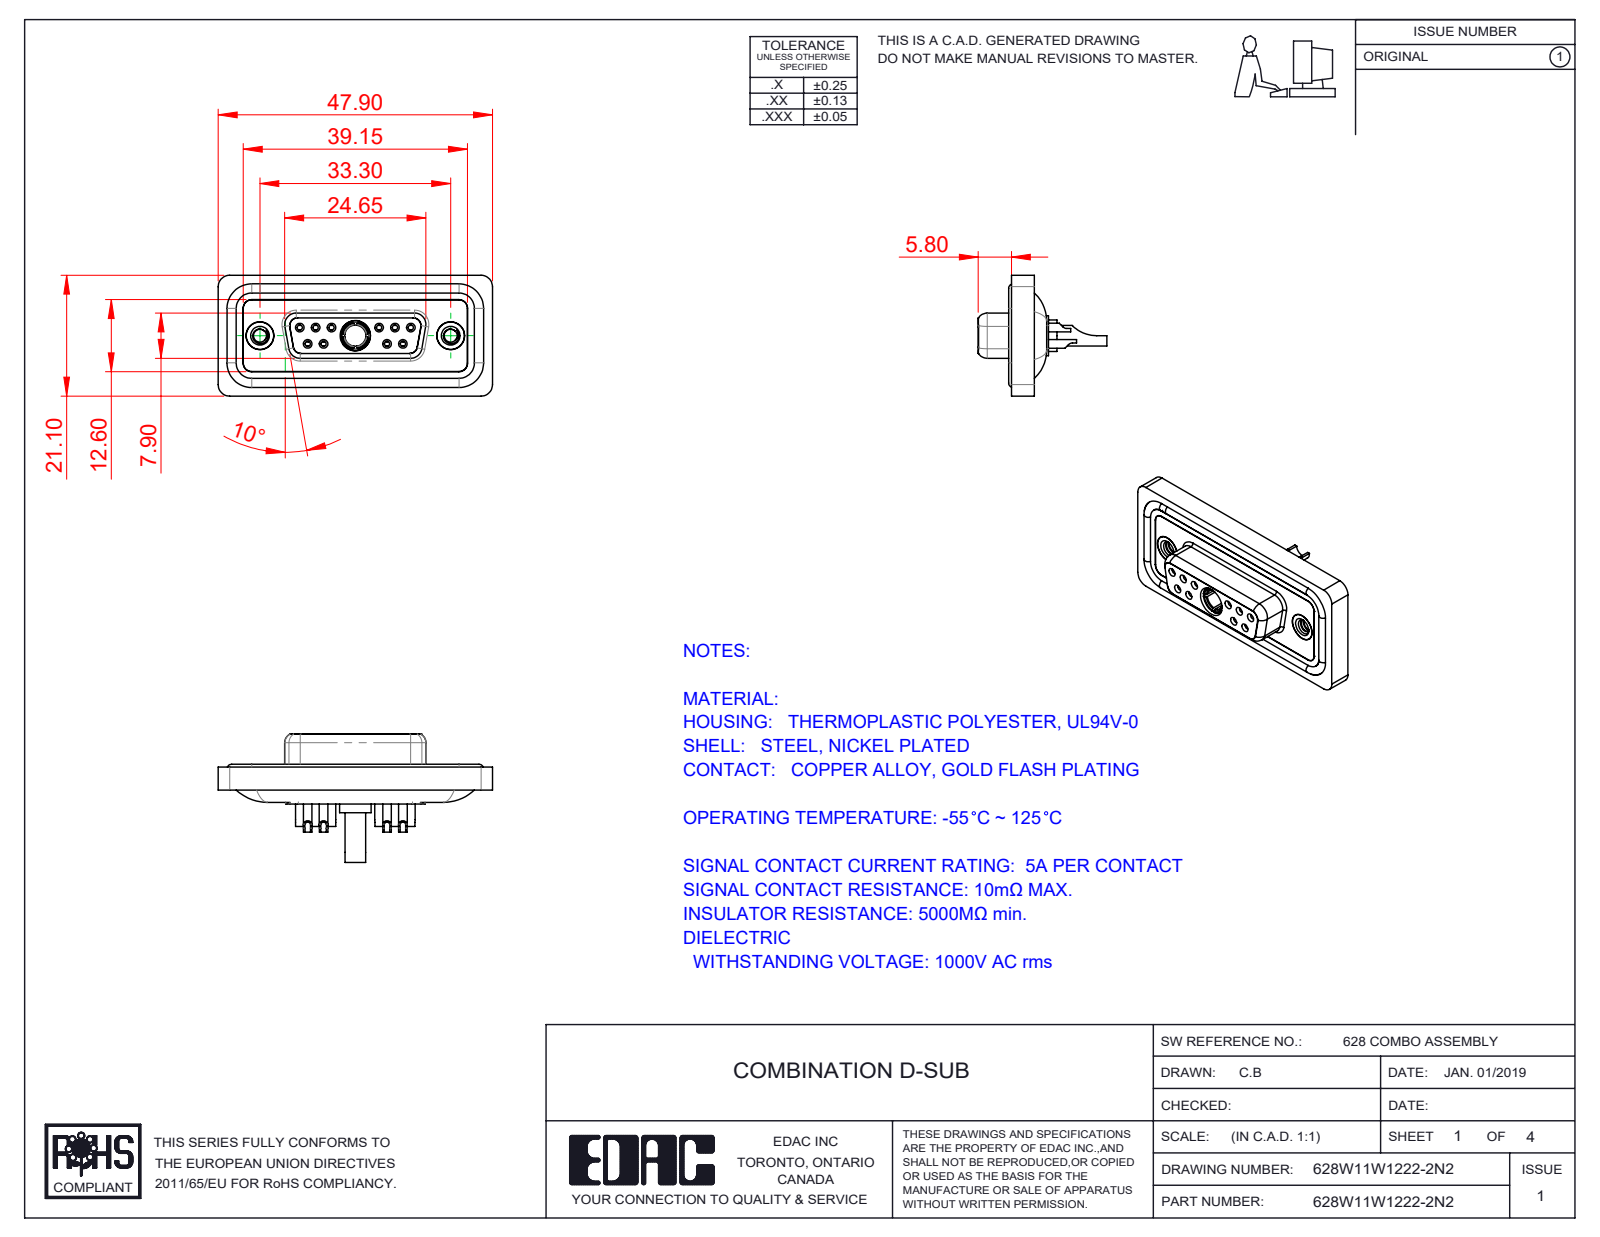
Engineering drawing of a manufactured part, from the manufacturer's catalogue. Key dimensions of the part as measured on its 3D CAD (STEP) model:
Part name (STEP PRODUCT): 628Combo Shell Rear_15 Contacts; Power Socket_20A SC; 628Combo Shell Front_15 Contacts; 628W11W1222-2N2 (+5 more)
STEP written by: SolidWorks 2020 (CONFIG_CONTROL_DESIGN)
Units: millimetres
Bodies: 19 solids, 1017 faces (307 planar, 424 cylindrical, 286 other)
Overall size (bounding box): 47.9 × 22.45 × 21.1
Volume: 6 158 mm³ · Surface area: 10 215 mm²
Round holes (diameter × count): ⌀0.9 ×10, ⌀1 ×10, ⌀1.1 ×10, ⌀1.5 ×10, ⌀2 ×10, ⌀1.7 ×6, ⌀1.6 ×4, ⌀4.85 ×3, ⌀2.26 ×2, ⌀4 ×2, ⌀4.05 ×2, ⌀5 ×2
Round bosses / shafts (diameter × count): ⌀2.2 ×10, ⌀1.6 ×10, ⌀4.95 ×2, ⌀4.8 ×2, ⌀5.5 ×1, ⌀5.2 ×1, ⌀4.96 ×1, ⌀4.75 ×1
Partial cylindrical surfaces — rounded edges, fillets, slot ends (radius × count): R1.5 ×22, R2 ×20, R1.35 ×12, R1.6 ×8, R1 ×6, R0.25 ×4, R0.5 ×4, R0.6 ×4
Main face-to-face distances: 0.4, 1.6, 1.8, 2.9, 0.5, 1.1, 5.65, 7.45, 6.6, 7.05
Hole centre spacings: 3.16, 2.77, 13.85, 11.08, 16.62, 5.03, 5.04, 5.54
